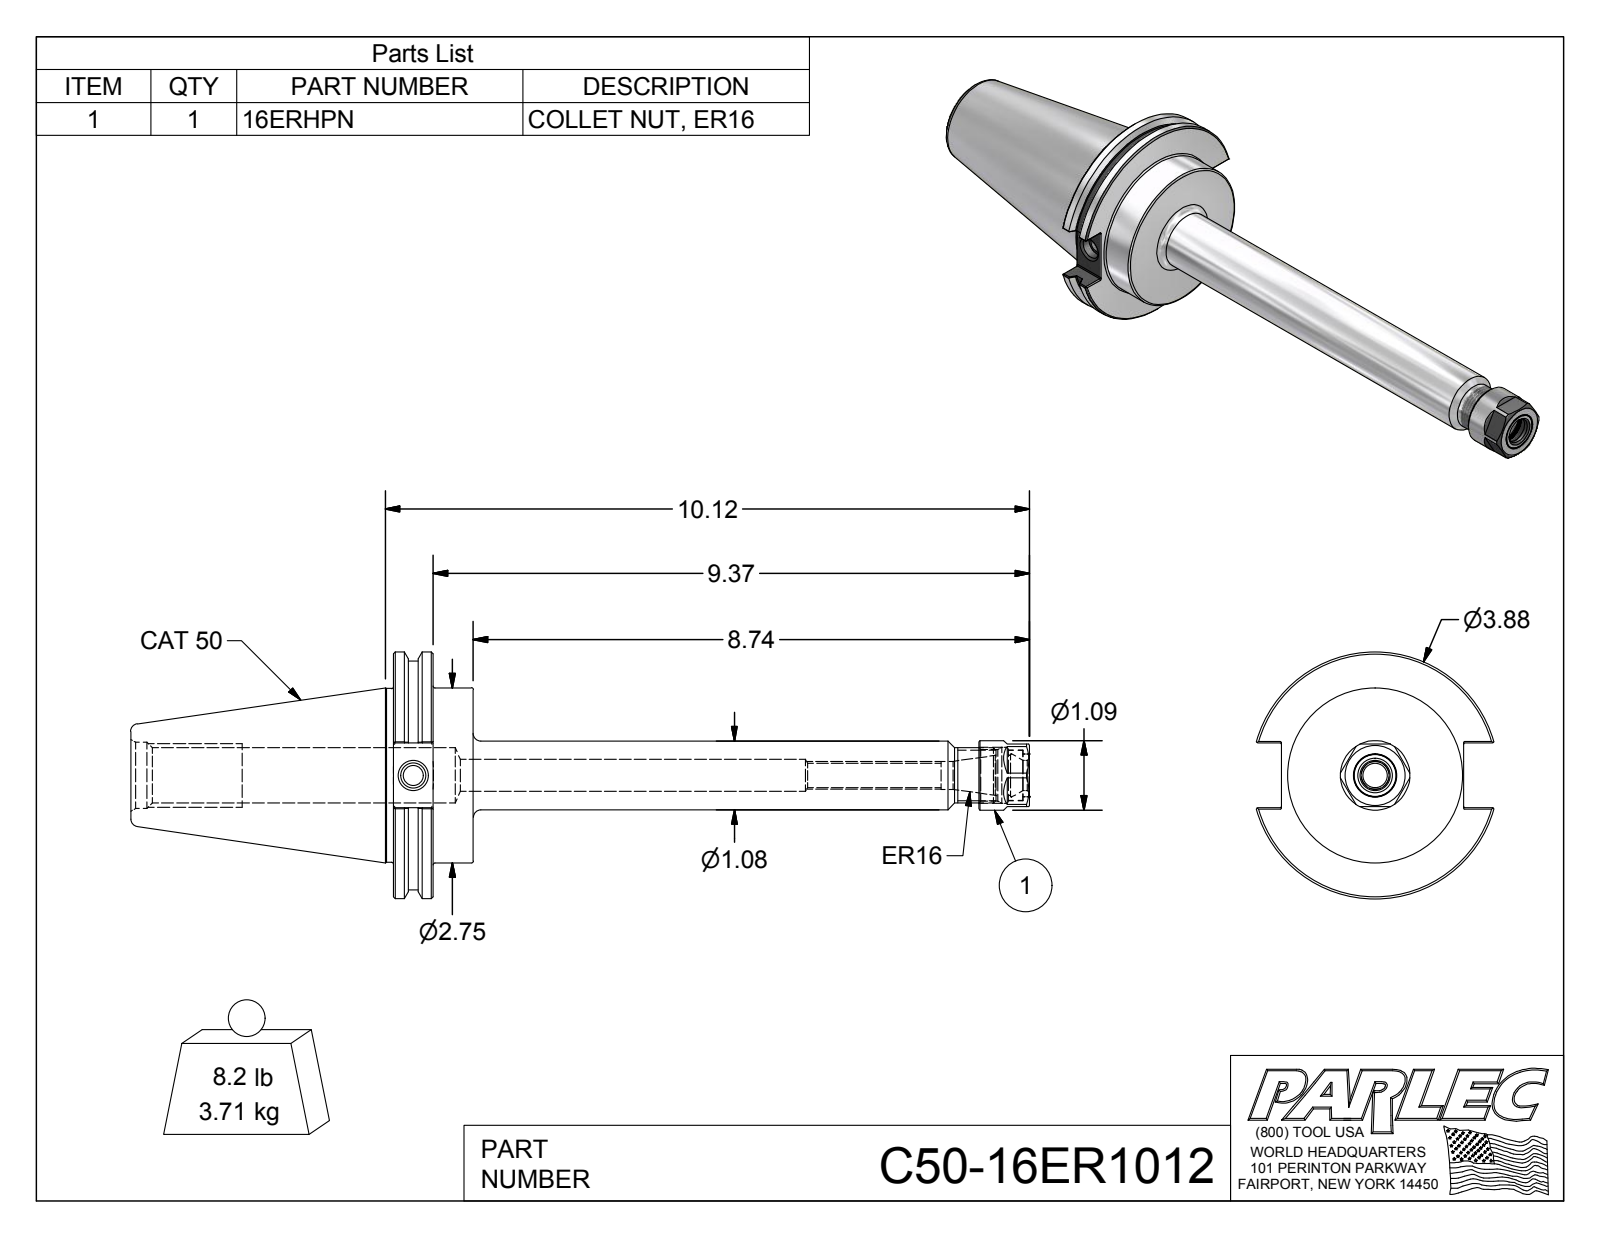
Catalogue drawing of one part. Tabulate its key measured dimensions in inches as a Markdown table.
| quantity | value |
| --- | --- |
| part name | C50-16ER1012; C50-16ER10-1; 16ERHPN |
| STEP written by | Autodesk Inventor 2012 (AUTOMOTIVE_DESIGN) |
| units | inches |
| bodies | 3 solids, 138 faces (53 planar, 39 cylindrical, 46 other) |
| overall size | 14.12 × 3.875 × 3.729 |
| volume | 29.05 in³ |
| surface area | 122.1 in² |
| round holes (diameter × count) | 0.315 × 1, 0.383 × 1, 0.399 × 1, 0.44 × 1, 0.474 × 1, 0.5 × 1, 0.63 × 1, 0.674 × 1, 0.68 × 1, 0.794 × 1, 0.814 × 1, 0.865 × 1 |
| round bosses / shafts (diameter × count) | 3.875 × 1, 3.594 × 1, 2.75 × 1, 2.73 × 1, 1.092 × 1, 1.08 × 1, 0.866 × 1, 0.79 × 1 |
| partial cylindrical surfaces (radius × count) | 0.02 × 12 |
| main face-to-face distances | 1.255, 0.625, 0.63, 4.125, 4.75, 5.38, 0.98, 14.12, 9.995, 9.37 |
